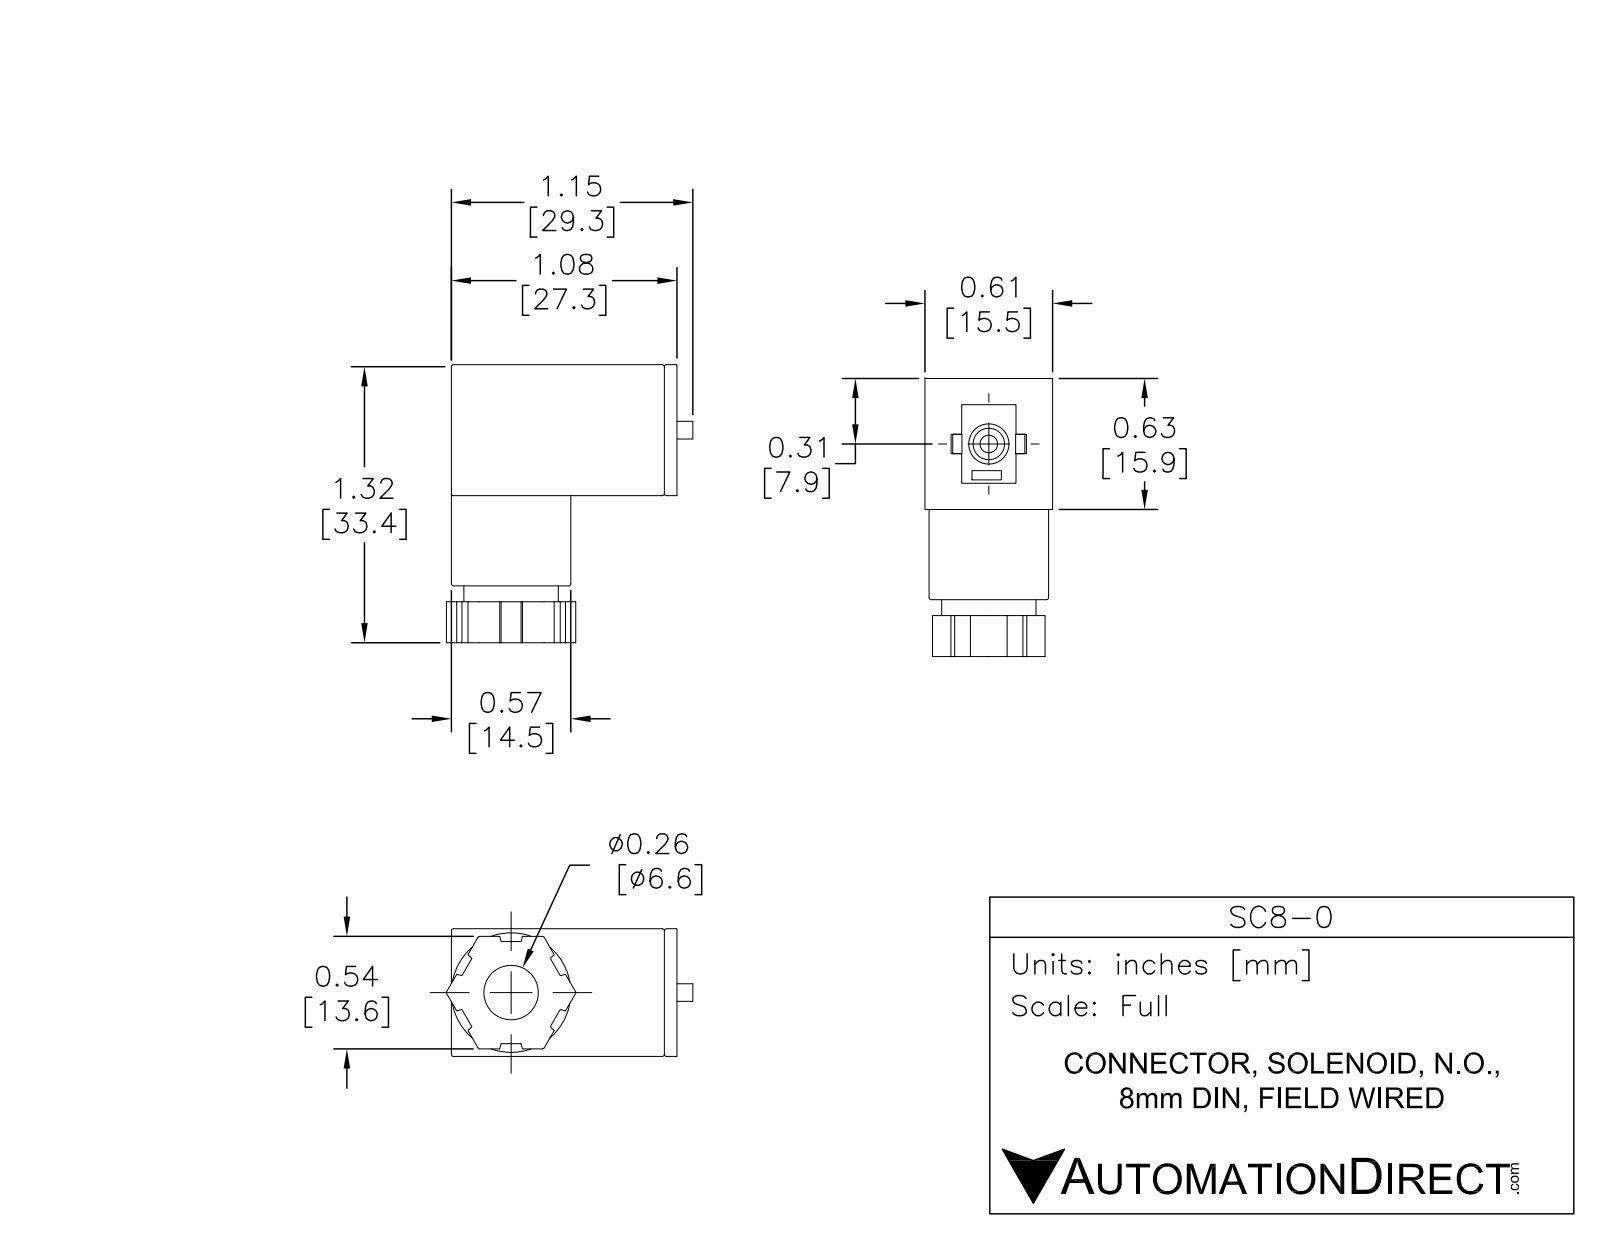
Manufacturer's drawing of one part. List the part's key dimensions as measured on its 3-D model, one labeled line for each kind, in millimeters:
Part name (STEP PRODUCT): SC8-0
STEP written by: SolidWorks 2015 (AUTOMOTIVE_DESIGN)
Units: millimetres
Bodies: 2 solids, 89 faces (58 planar, 26 cylindrical, 5 other)
Overall size (bounding box): 33.92 × 26.48 × 15.48
Volume: 7 855 mm³ · Surface area: 4 168 mm²
Round holes (diameter × count): ⌀2.98 ×1, ⌀5 ×1, ⌀6.7 ×1, ⌀7.15 ×1
Round bosses / shafts (diameter × count): ⌀14.5 ×1, ⌀11.8 ×1, ⌀6.5 ×1, ⌀2.5 ×1
Partial cylindrical surfaces — rounded edges, fillets, slot ends (radius × count): R0.5 ×4, R1.4 ×4
Main face-to-face distances: 15.48, 15.87, 24.9, 33.92, 18.05, 13.82, 0.9, 0.83, 14.65, 28.97
